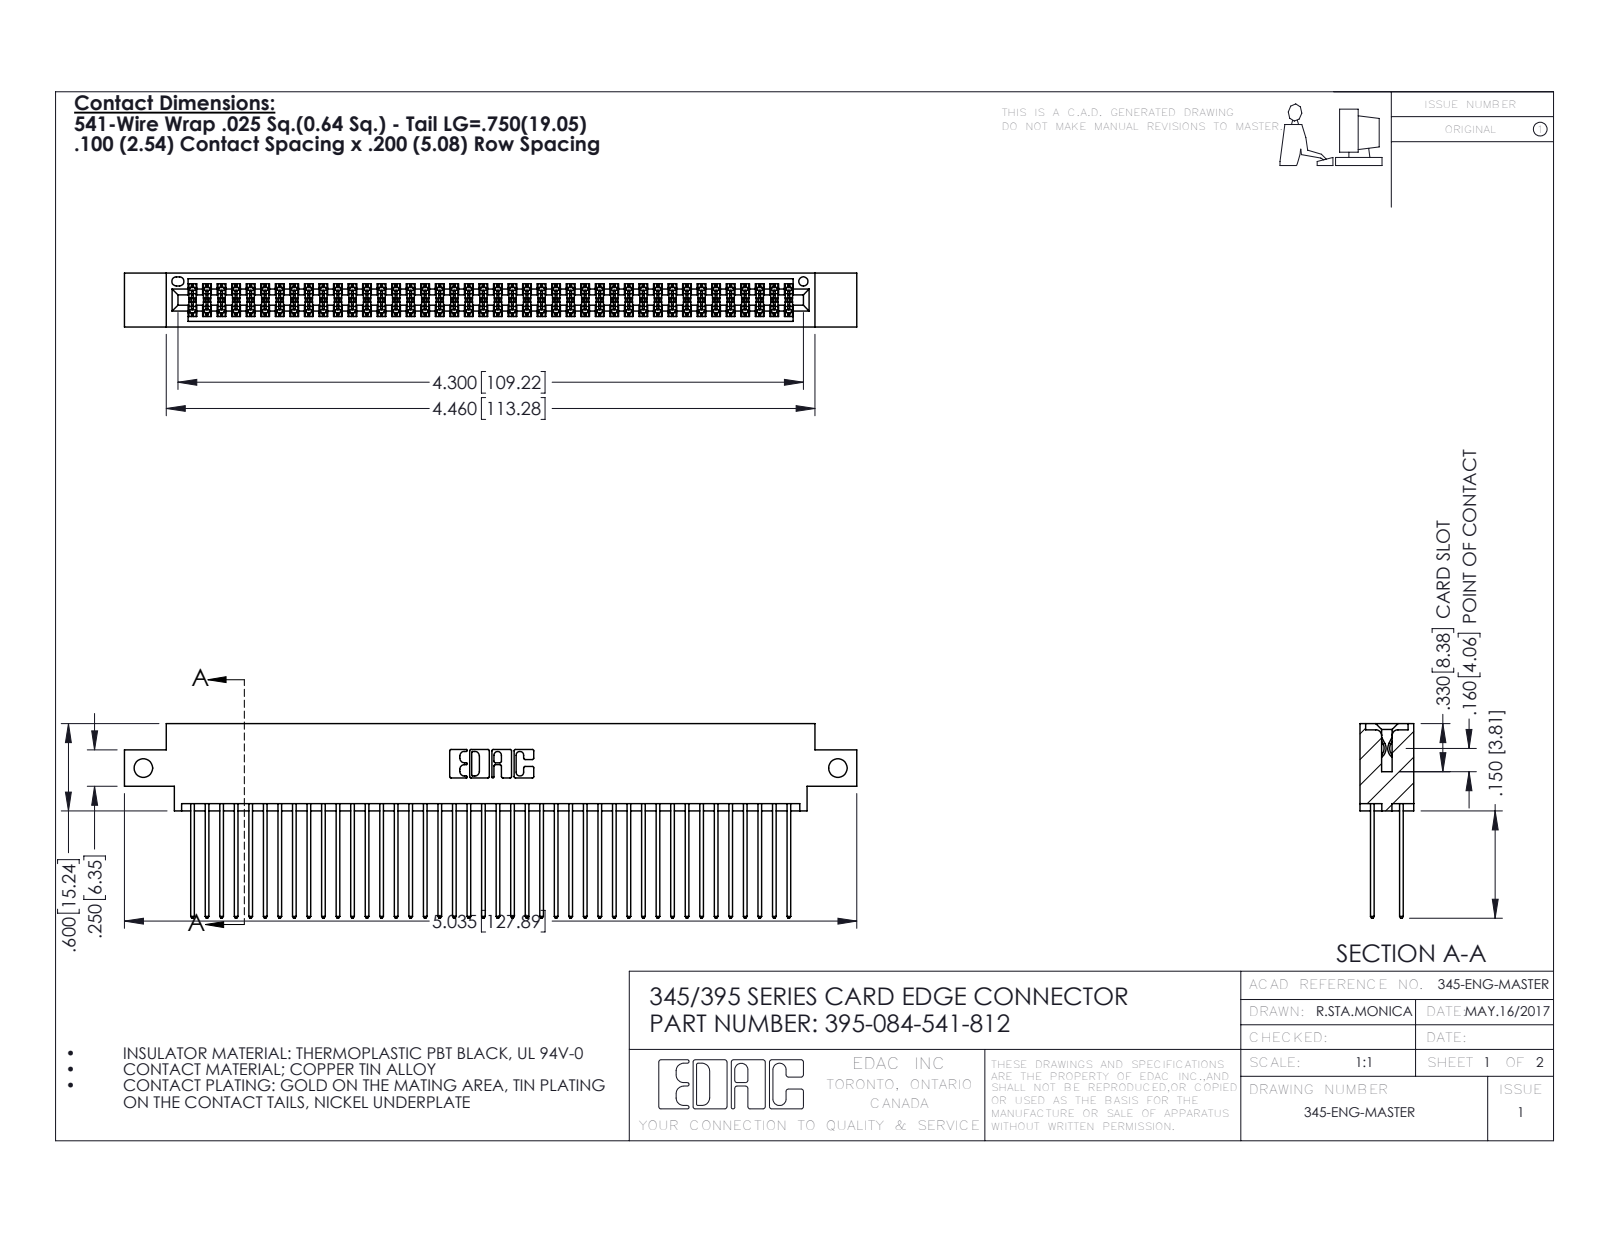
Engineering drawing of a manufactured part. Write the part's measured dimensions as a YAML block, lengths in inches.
part_name: "395-084-541-812; 345 Part_0.170 Offset - Side Mount; 345-292-001_345-293-141"
step_written_by: "SolidWorks 2016 (CONFIG_CONTROL_DESIGN)"
units: inches
bodies: {solids: 85, faces: 4330, planar: 2856, cylindrical: 1474, other: 0}
overall_size: [5.035, 1.337, 0.37]
volume: 0.775
surface_area: 32.63
round_holes:
  - {diameter: 0.128, count: 2}
  - {diameter: 0.064, count: 1}
partial_cylinders:
  - {radius: 0.006, count: 126}
  - {radius: 0.01, count: 84}
  - {radius: 0.01, count: 22}
  - {radius: 0.007, count: 6}
  - {radius: 0.031, count: 6}
  - {radius: 0.026, count: 3}
  - {radius: 0.014, count: 2}
  - {radius: 0.019, count: 2}
face_to_face_distances: [0.298, 0.072, 0.2, 0.098, 0.272, 0.025, 0.37, 0.225, 0.175, 0.149]
hole_center_spacings: [4.775]
